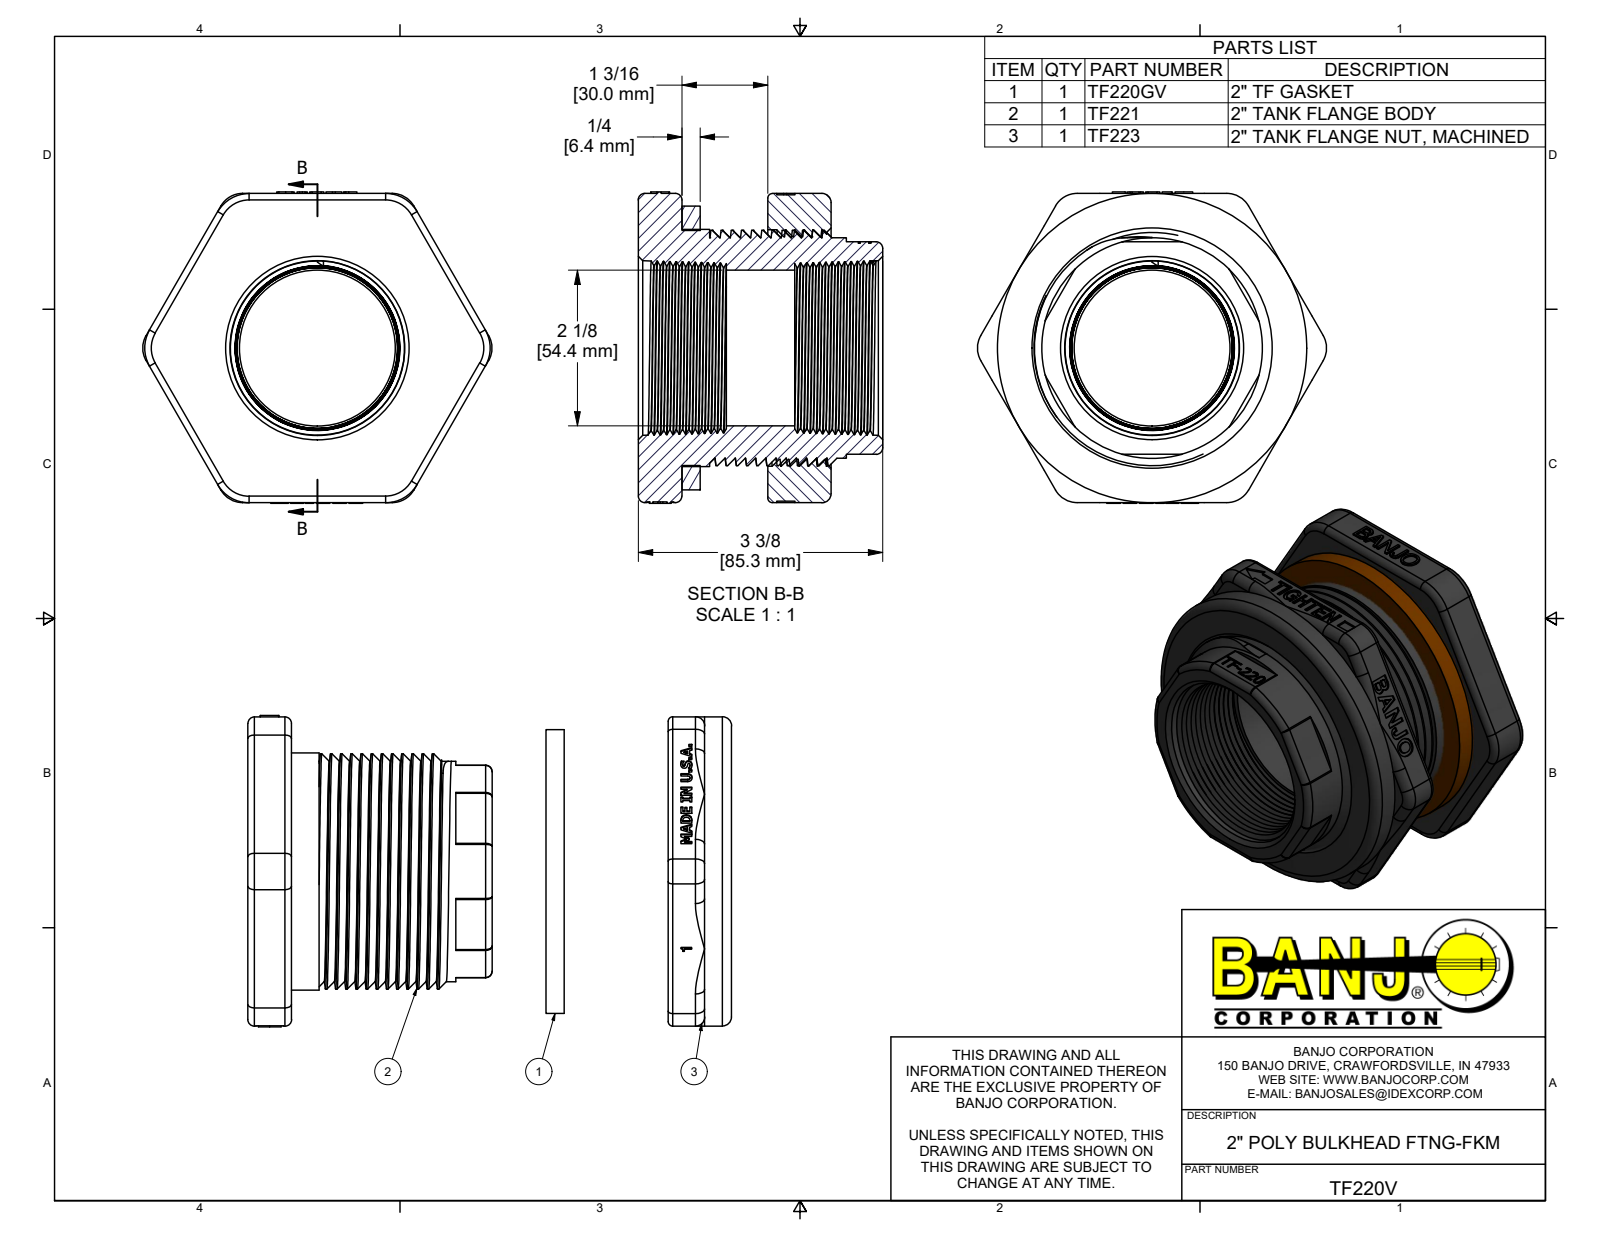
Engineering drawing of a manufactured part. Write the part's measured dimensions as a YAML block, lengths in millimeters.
part_name: "TF220V; TF221; TF223; TF223X (+1 more)"
step_written_by: "Autodesk Inventor 2019 (AUTOMOTIVE_DESIGN)"
units: millimeters
bodies: {solids: 3, faces: 898, planar: 507, cylindrical: 106, other: 285}
overall_size: [121.9, 108.7, 85.3]
volume: 381500
surface_area: 107400
round_holes:
  - {diameter: 54.4, count: 1}
  - {diameter: 77.6, count: 1}
  - {diameter: 82, count: 1}
  - {diameter: 82.6, count: 1}
round_bosses_or_shafts:
  - {diameter: 108, count: 1}
  - {diameter: 99.1, count: 1}
  - {diameter: 82.8, count: 1}
  - {diameter: 82.2, count: 1}
  - {diameter: 77, count: 1}
partial_cylinders:
  - {radius: 2.3, count: 18}
  - {radius: 1.5, count: 12}
  - {radius: 1.6, count: 6}
  - {radius: 3.2, count: 6}
  - {radius: 8.7, count: 6}
  - {radius: 12.7, count: 6}
  - {radius: 25.4, count: 1}
face_to_face_distances: [15.2, 45.2, 30, 67.3, 52.1, 22.1, 6.4, 21.6, 23.6, 45.7]
